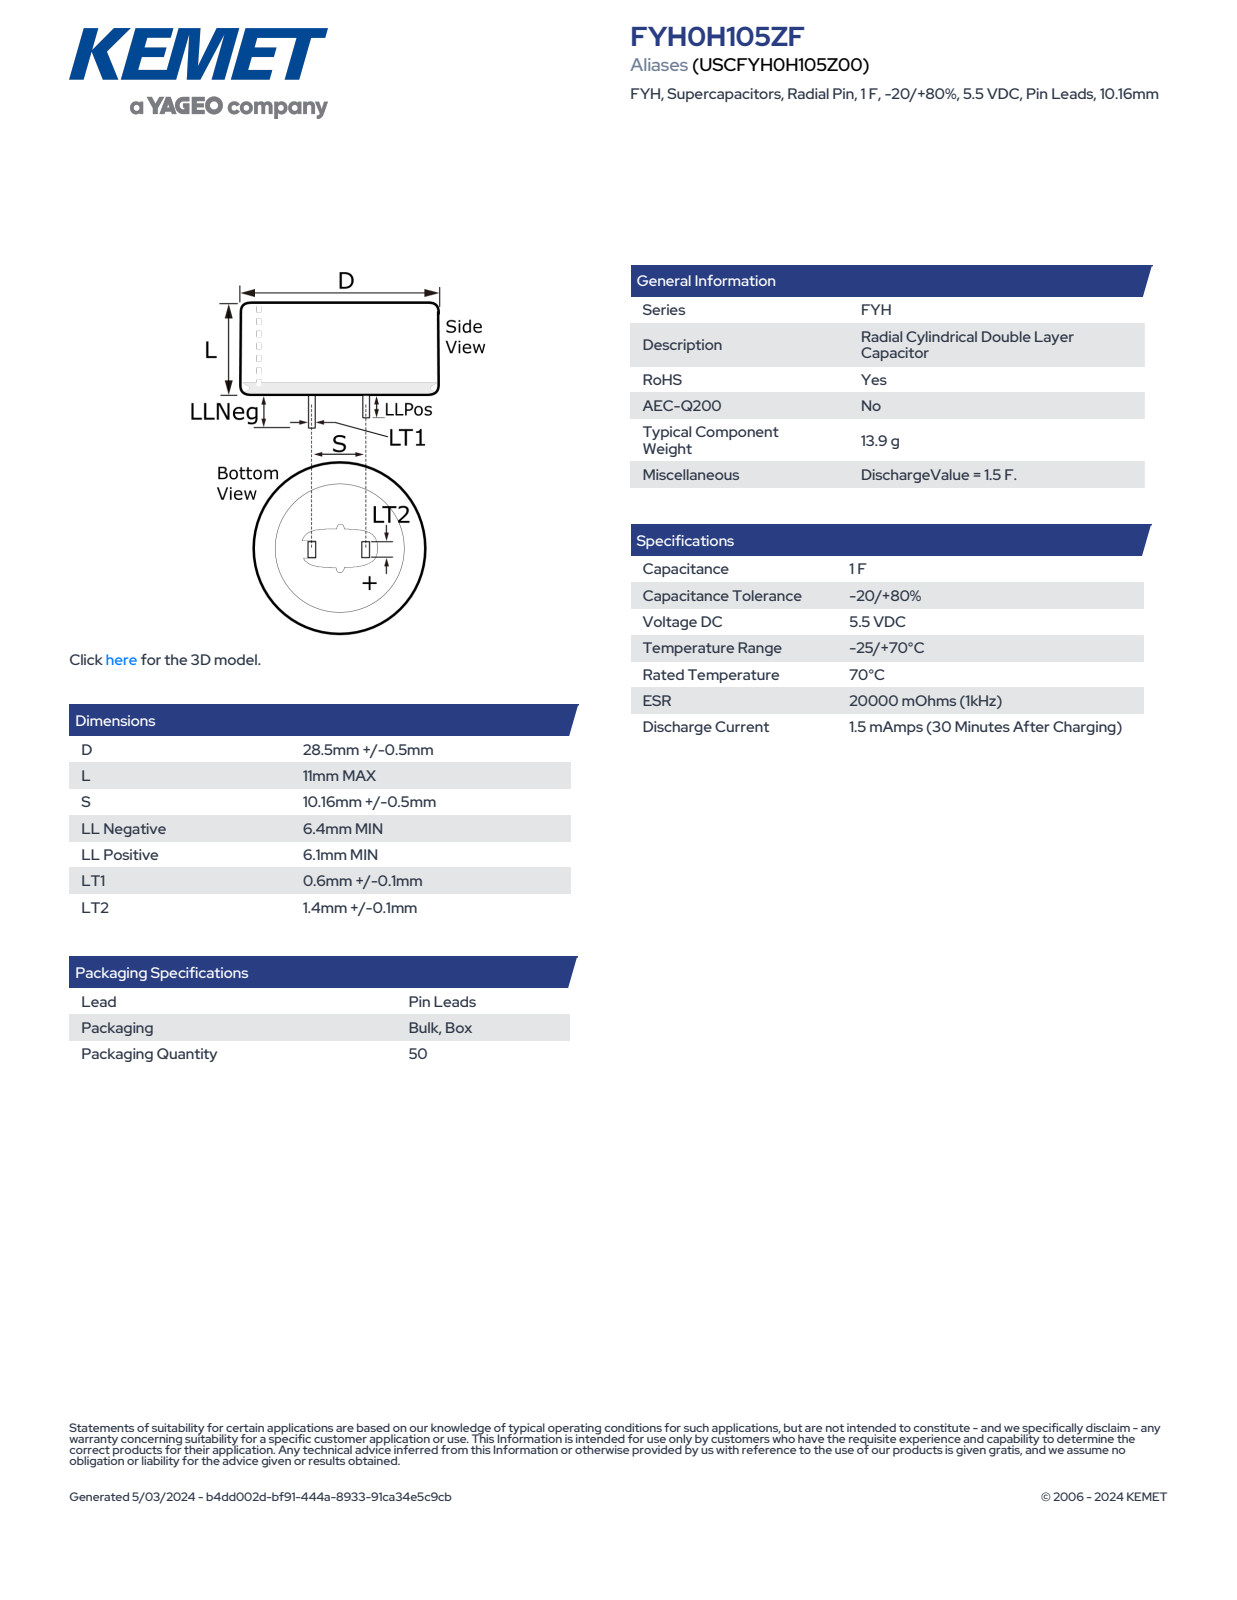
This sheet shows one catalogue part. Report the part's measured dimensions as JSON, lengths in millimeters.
{"part_name": "CDR_LPLLN_D29L11S10.16LLNEG6.4LLPOS6.1LT10.7LT21.5", "step_written_by": "SolidWorks 2014 (AUTOMOTIVE_DESIGN)", "units": "millimeters", "bodies": {"solids": 1, "faces": 78, "planar": 70, "cylindrical": 4, "other": 4}, "overall_size": [29, 29, 17.4], "volume_mm3": 7260, "surface_area_mm2": 2323, "round_bosses_or_shafts": [[29, 1]], "partial_cylinders_radius": [[14.51, 1]], "face_to_face_distances": [11, 0.7, 10.16, 10.99, 10.86, 9.46, 1.5, 6.4, 17.39, 17.4]}
